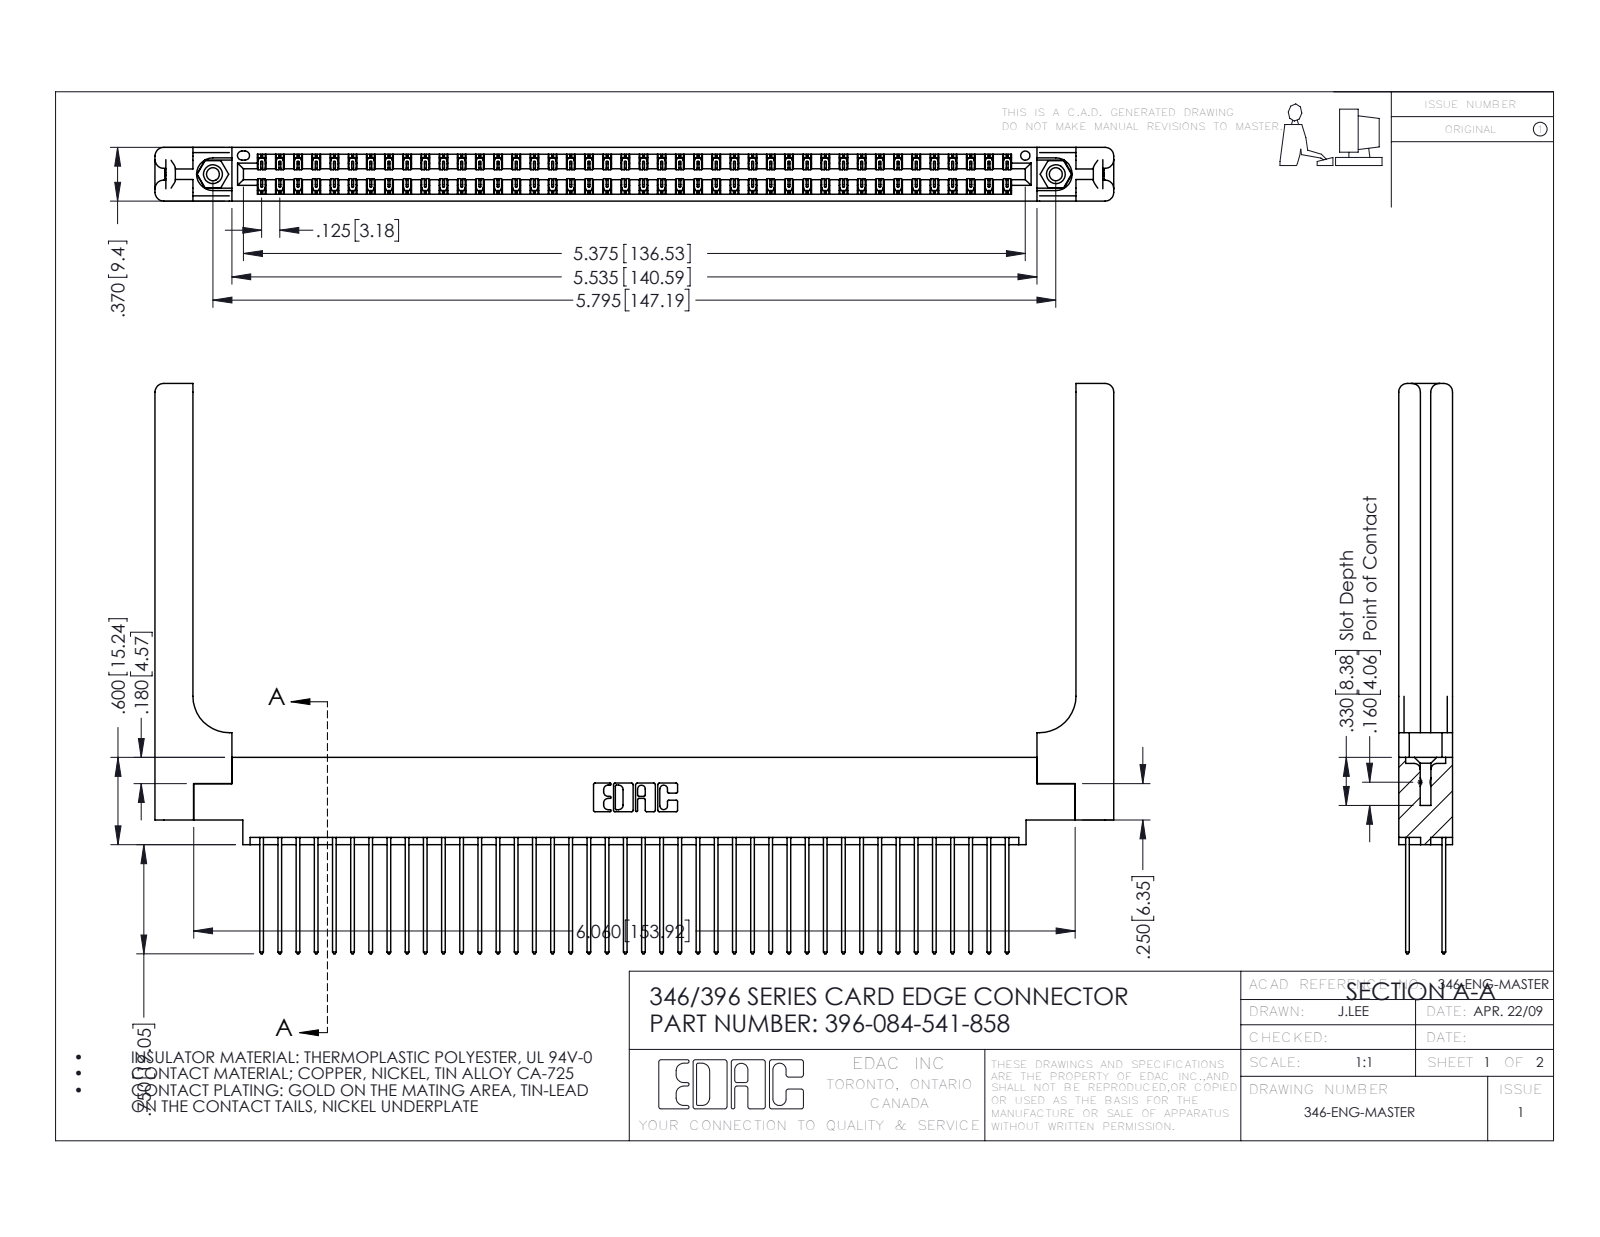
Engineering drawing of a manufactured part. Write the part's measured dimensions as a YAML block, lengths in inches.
part_name: "345-250-001_345-250-001-102; 396-084-541-858; 346 Part_0.170 Offset - 0.156 Dia-TH; 345-292-001_345-293-141 (+1 more)"
step_written_by: "SolidWorks 2016 (CONFIG_CONTROL_DESIGN)"
units: inches
bodies: {solids: 89, faces: 4750, planar: 3168, cylindrical: 1522, other: 60}
overall_size: [6.591, 3.92, 0.37]
volume: 1.473
surface_area: 47.05
round_holes:
  - {diameter: 0.089, count: 2}
  - {diameter: 0.125, count: 2}
  - {diameter: 0.156, count: 2}
  - {diameter: 0.064, count: 1}
round_bosses_or_shafts:
  - {diameter: 0.155, count: 2}
partial_cylinders:
  - {radius: 0.006, count: 126}
  - {radius: 0.01, count: 84}
  - {radius: 0.01, count: 22}
  - {radius: 0.06, count: 16}
  - {radius: 0.007, count: 6}
  - {radius: 0.031, count: 6}
  - {radius: 0.026, count: 3}
  - {radius: 0.014, count: 2}
face_to_face_distances: [0.048, 0.322, 0.072, 0.37, 0.25, 0.025, 0.298, 0.148, 0.15, 0.275]
hole_center_spacings: [0.246, 5.586, 5.795]
